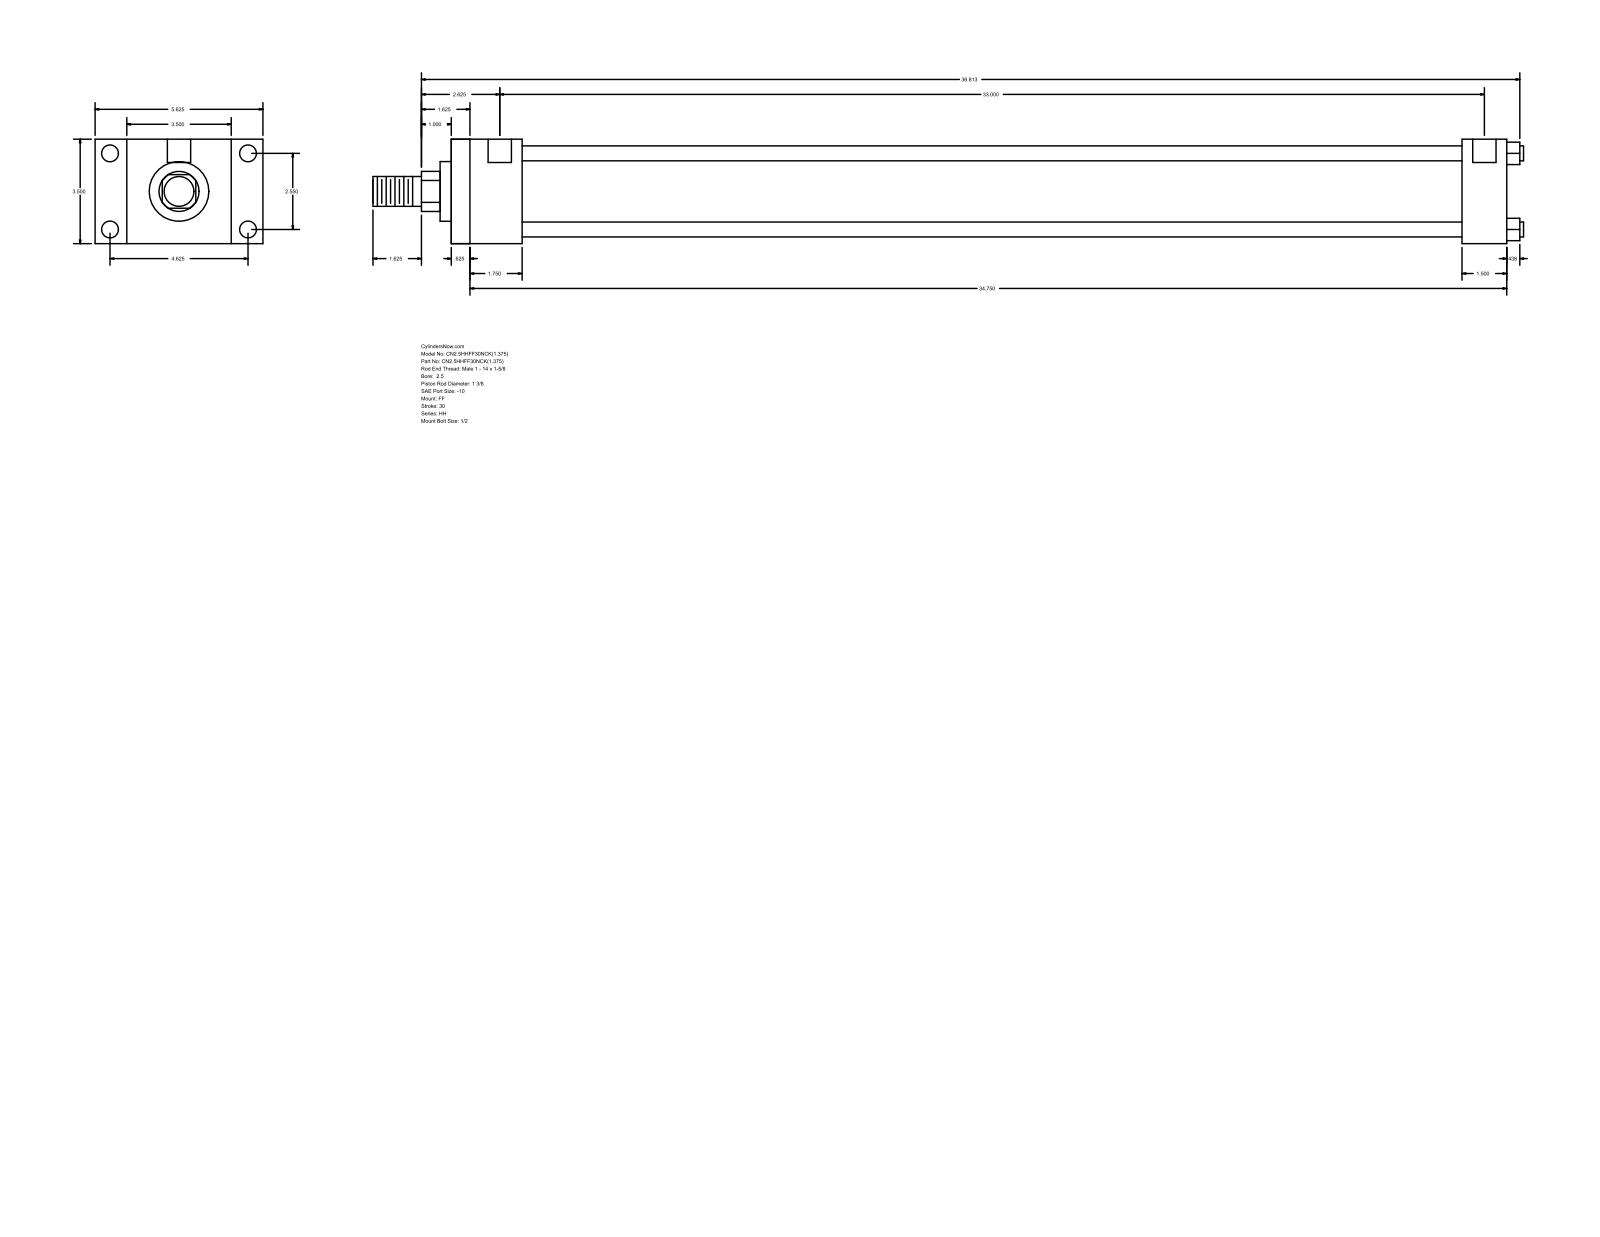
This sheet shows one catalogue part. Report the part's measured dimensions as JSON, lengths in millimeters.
{"part_name": "HH_FF__0250_1.375", "step_written_by": "GSSL Pune (CONFIG_CONTROL_DESIGN)", "units": "millimeters", "bodies": {"solids": 0, "faces": 92, "planar": 64, "cylindrical": 28, "other": 0}, "overall_size": [979.49, 142.88, 88.9], "round_holes": [[5.56, 4], [14.3, 4], [19.84, 2]], "round_bosses_or_shafts": [[12.7, 4], [73.03, 1], [50.8, 1], [34.92, 1], [25.4, 1]], "partial_cylinders_radius": [[17.06, 1]], "face_to_face_distances": [88.9, 898.52, 15.87, 882.65, 60.32, 44.45, 838.2, 860.43, 844.56, 800.11], "hole_center_spacings": [1.58, 64.76, 117.48, 134.15, 839.79, 841.37, 838.21]}
